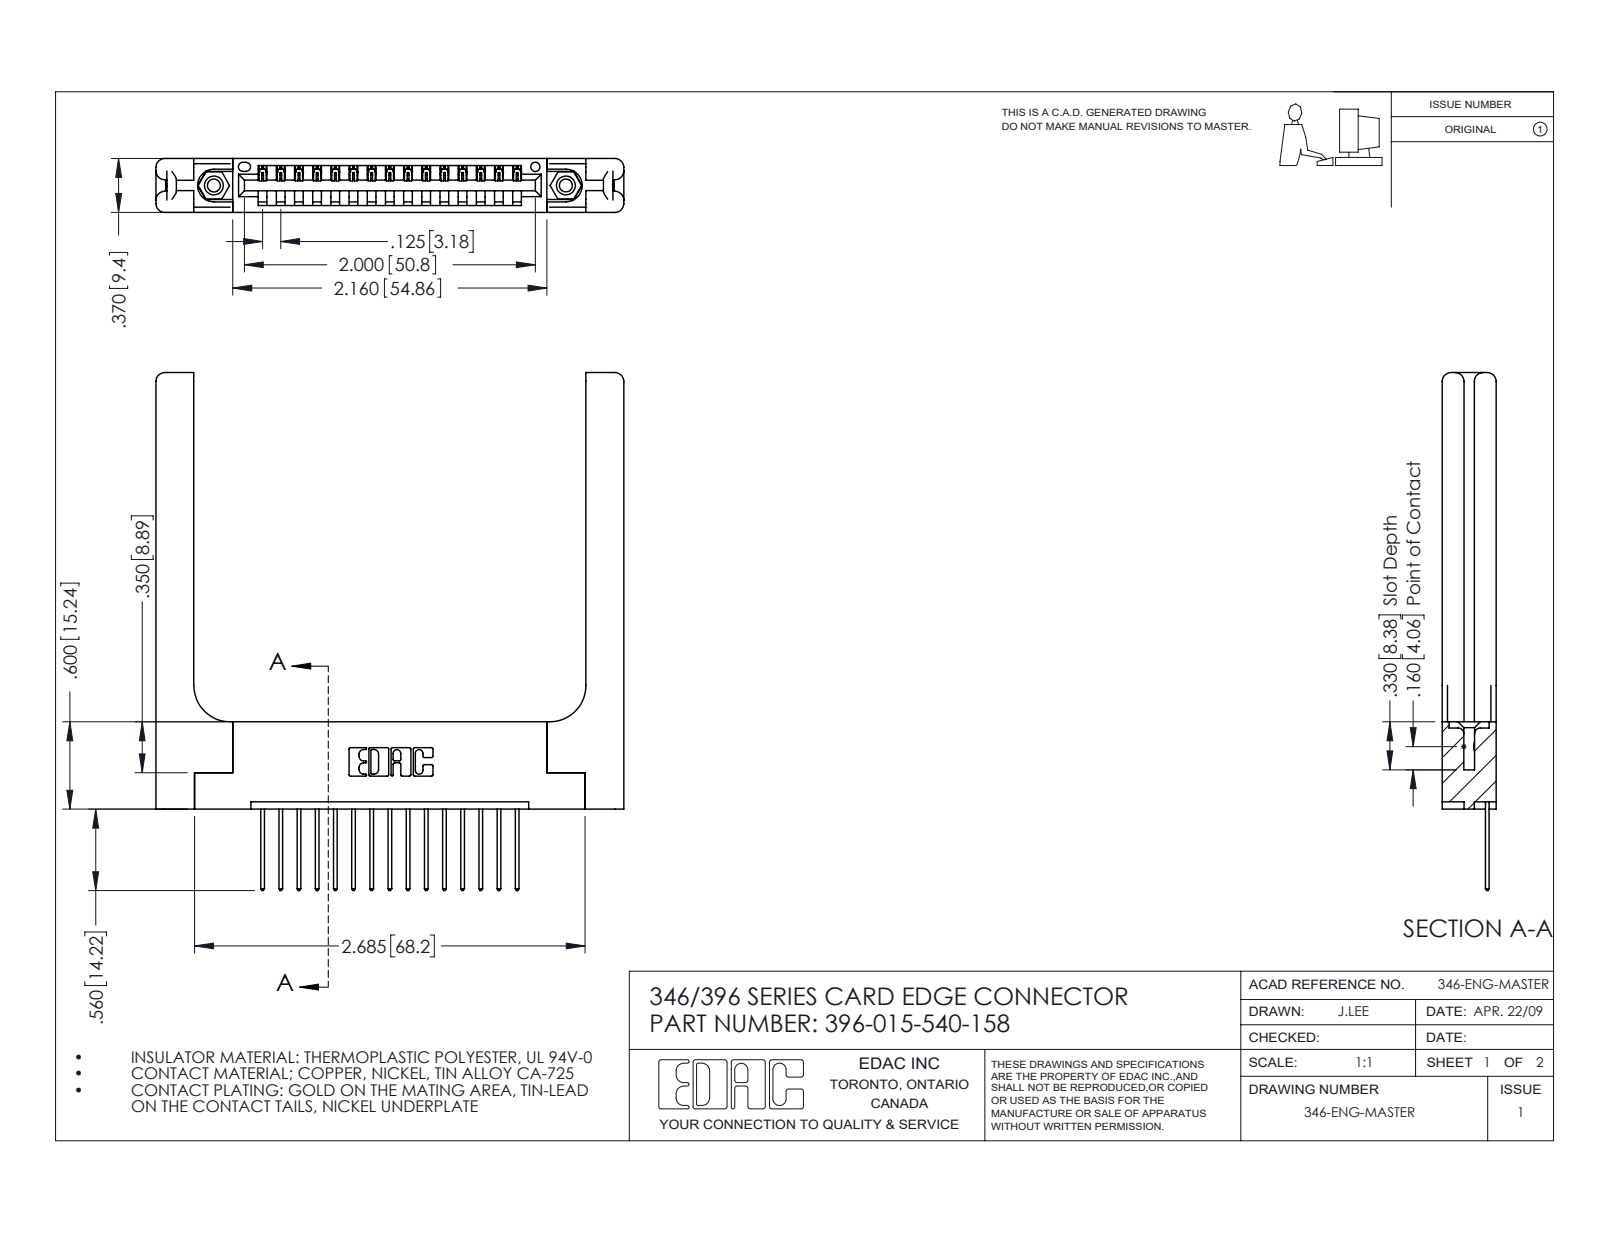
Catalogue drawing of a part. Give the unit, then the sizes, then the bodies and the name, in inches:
Units: inches
Overall size (bounding box): 3.56 × 3.216 × 0.37
Round holes (diameter × count): ⌀0.089 ×2, ⌀0.125 ×2, ⌀0.156 ×2, ⌀0.064 ×1
Round bosses / shafts (diameter × count): ⌀0.155 ×2
Partial cylindrical surfaces — rounded edges, fillets, slot ends (radius × count): R0.006 ×30, R0.01 ×30, R0.01 ×22, R0.06 ×16, R0.007 ×6, R0.031 ×6, R0.026 ×3, R0.03 ×2
Main face-to-face distances: 0.37, 0.15, 0.072, 0.148, 0.048, 0.322, 0.25, 0.22, 0.102, 0.173
Hole centre spacings: 0.246, 2.213, 2.42
Volume: 0.926 in³ · Surface area: 22.62 in²
Bodies: 20 solids, 1248 faces (824 planar, 364 cylindrical, 60 other)
Part name (STEP PRODUCT): 345-250-001_345-250-001-102; 396-015-540-158; 345-292-001_345-293-140; 346-220-058_345-220-058 (+1 more)
STEP written by: SolidWorks 2016 (CONFIG_CONTROL_DESIGN)
